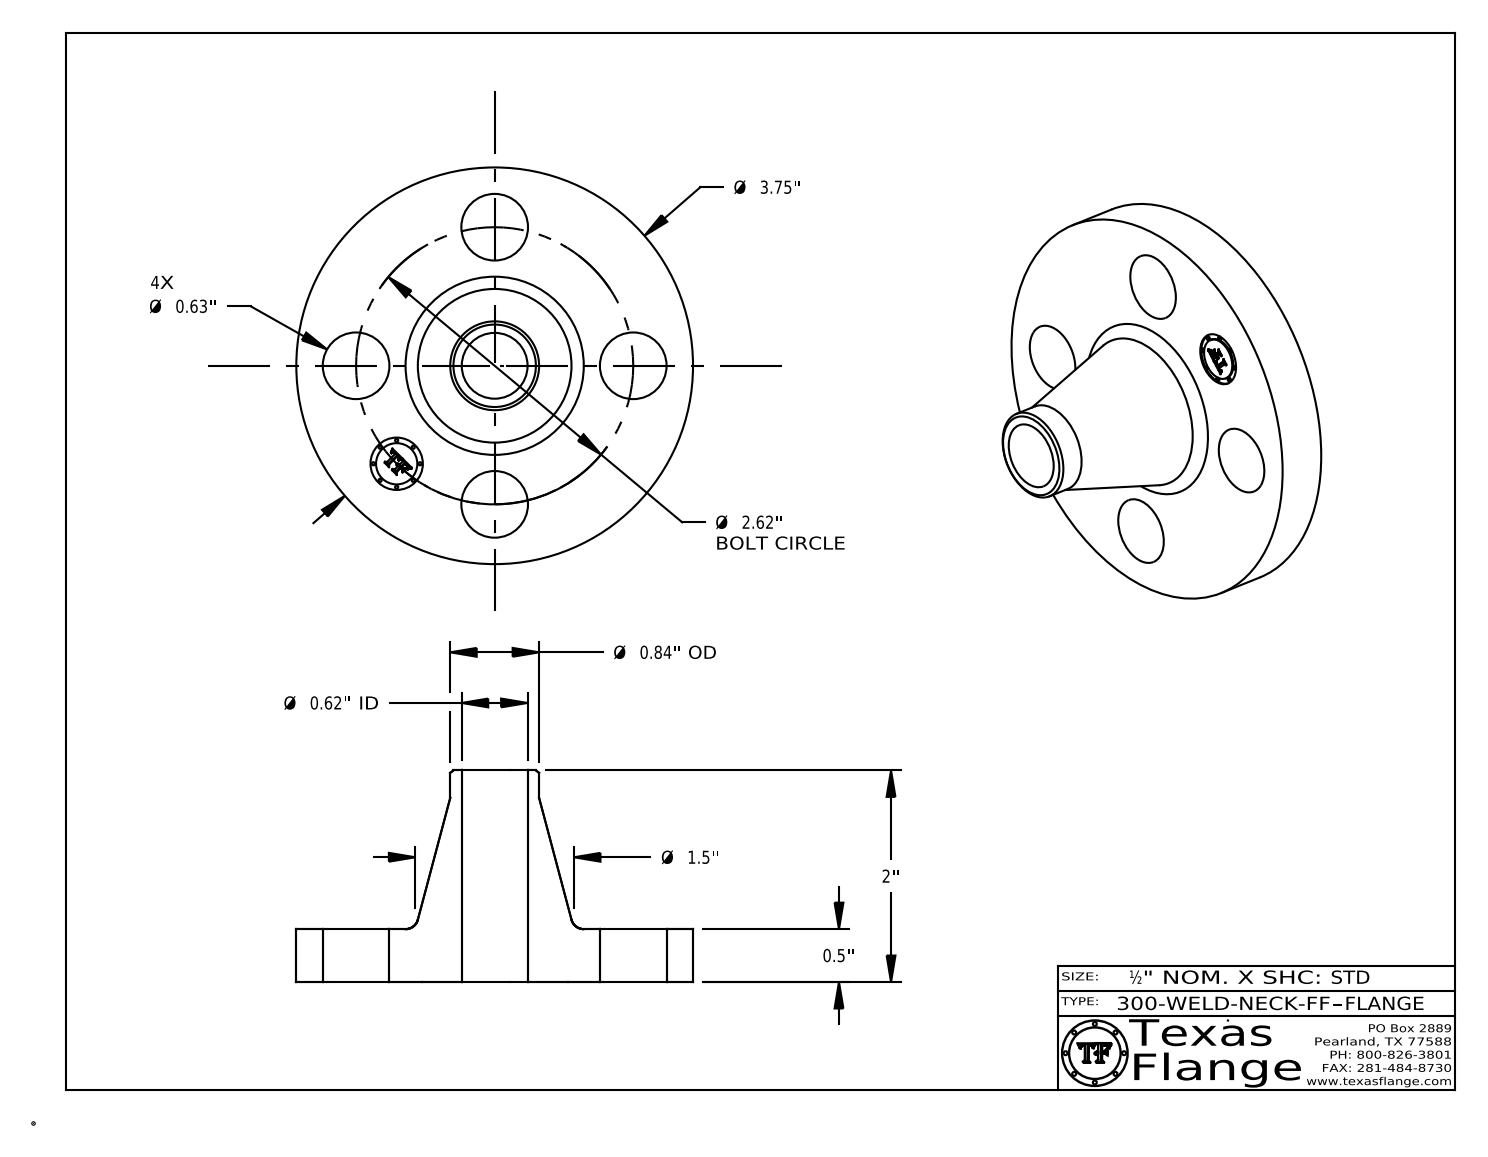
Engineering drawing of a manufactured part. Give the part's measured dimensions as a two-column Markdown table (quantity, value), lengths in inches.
| quantity | value |
| --- | --- |
| part name | 300-WELD-NECK-FF |
| STEP written by | CATIA V5 STEP AP214 (AUTOMOTIVE_DESIGN) |
| units | inches |
| bodies | 1 solid, 409 faces (369 planar, 34 cylindrical, 6 other) |
| overall size | 3.75 × 3.75 × 2 |
| volume | 5.81 in³ |
| surface area | 36.86 in² |
| round holes (diameter × count) | 0.63 × 4, 0.495 × 1, 0.622 × 1 |
| round bosses / shafts (diameter × count) | 0.03 × 8, 3.75 × 1, 0.84 × 1, 0.39 × 1 |
| main face-to-face distances | 0.5, 2, 1.5, 0.485, 0.015, 1.515, 0.148, 0.144, 0.027, 0.096 |
| hole center spacings | 1.31, 1.852, 1.003, 2.42, 2.62, 1.31 |
